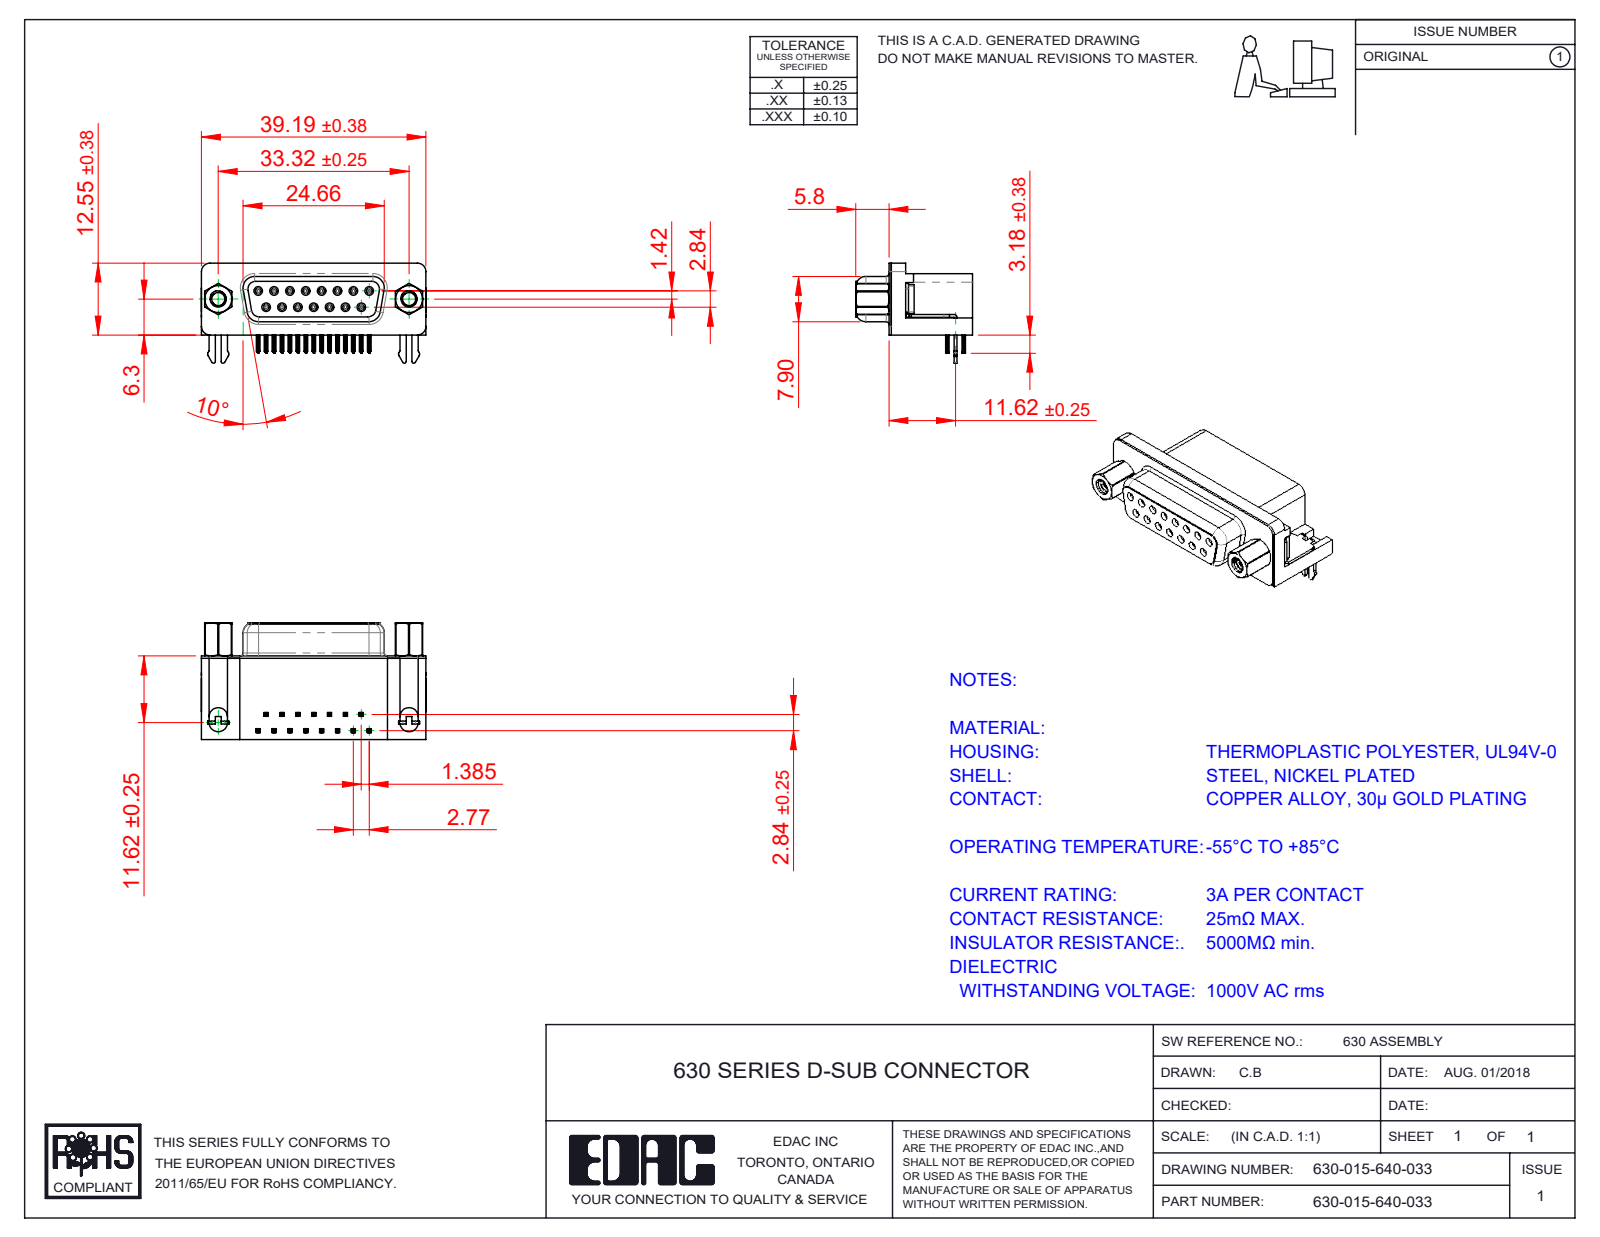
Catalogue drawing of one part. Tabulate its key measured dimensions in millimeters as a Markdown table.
| quantity | value |
| --- | --- |
| part name | 630 Housing_15 Socket; 630 Contact Top; 630 4-40 Threaded Rivet; 630 Shell_15 Socket (+4 more) |
| STEP written by | SolidWorks 2020 (CONFIG_CONTROL_DESIGN) |
| units | millimeters |
| bodies | 23 solids, 2591 faces (1126 planar, 685 cylindrical, 780 other) |
| overall size | 39.22 × 20.4 × 17.48 |
| volume | 6 073 mm³ |
| surface area | 7 688 mm² |
| round holes (diameter × count) | 0.8 × 15, 0.9 × 15, 2.26 × 2, 2.29 × 2, 4 × 2, 4.8 × 2, 5 × 2 |
| round bosses / shafts (diameter × count) | 1.2 × 15, 4.9 × 2, 4.75 × 2, 3.9 × 2, 2.79 × 2 |
| partial cylindrical surfaces (radius × count) | 0.1 × 120, 0.15 × 60, 0.35 × 30, 1 × 18, 0.34 × 15, 0.5 × 10, 0.25 × 8, 1.35 × 8 |
| main face-to-face distances | 0.4, 6.2, 2.73, 14.2, 10.35, 14.6, 2.9, 3.18, 5.8, 6.65 |
| hole center spacings | 3.16, 2.77, 5.54, 5.03, 5.04, 7.48, 7.49, 8.31 |
